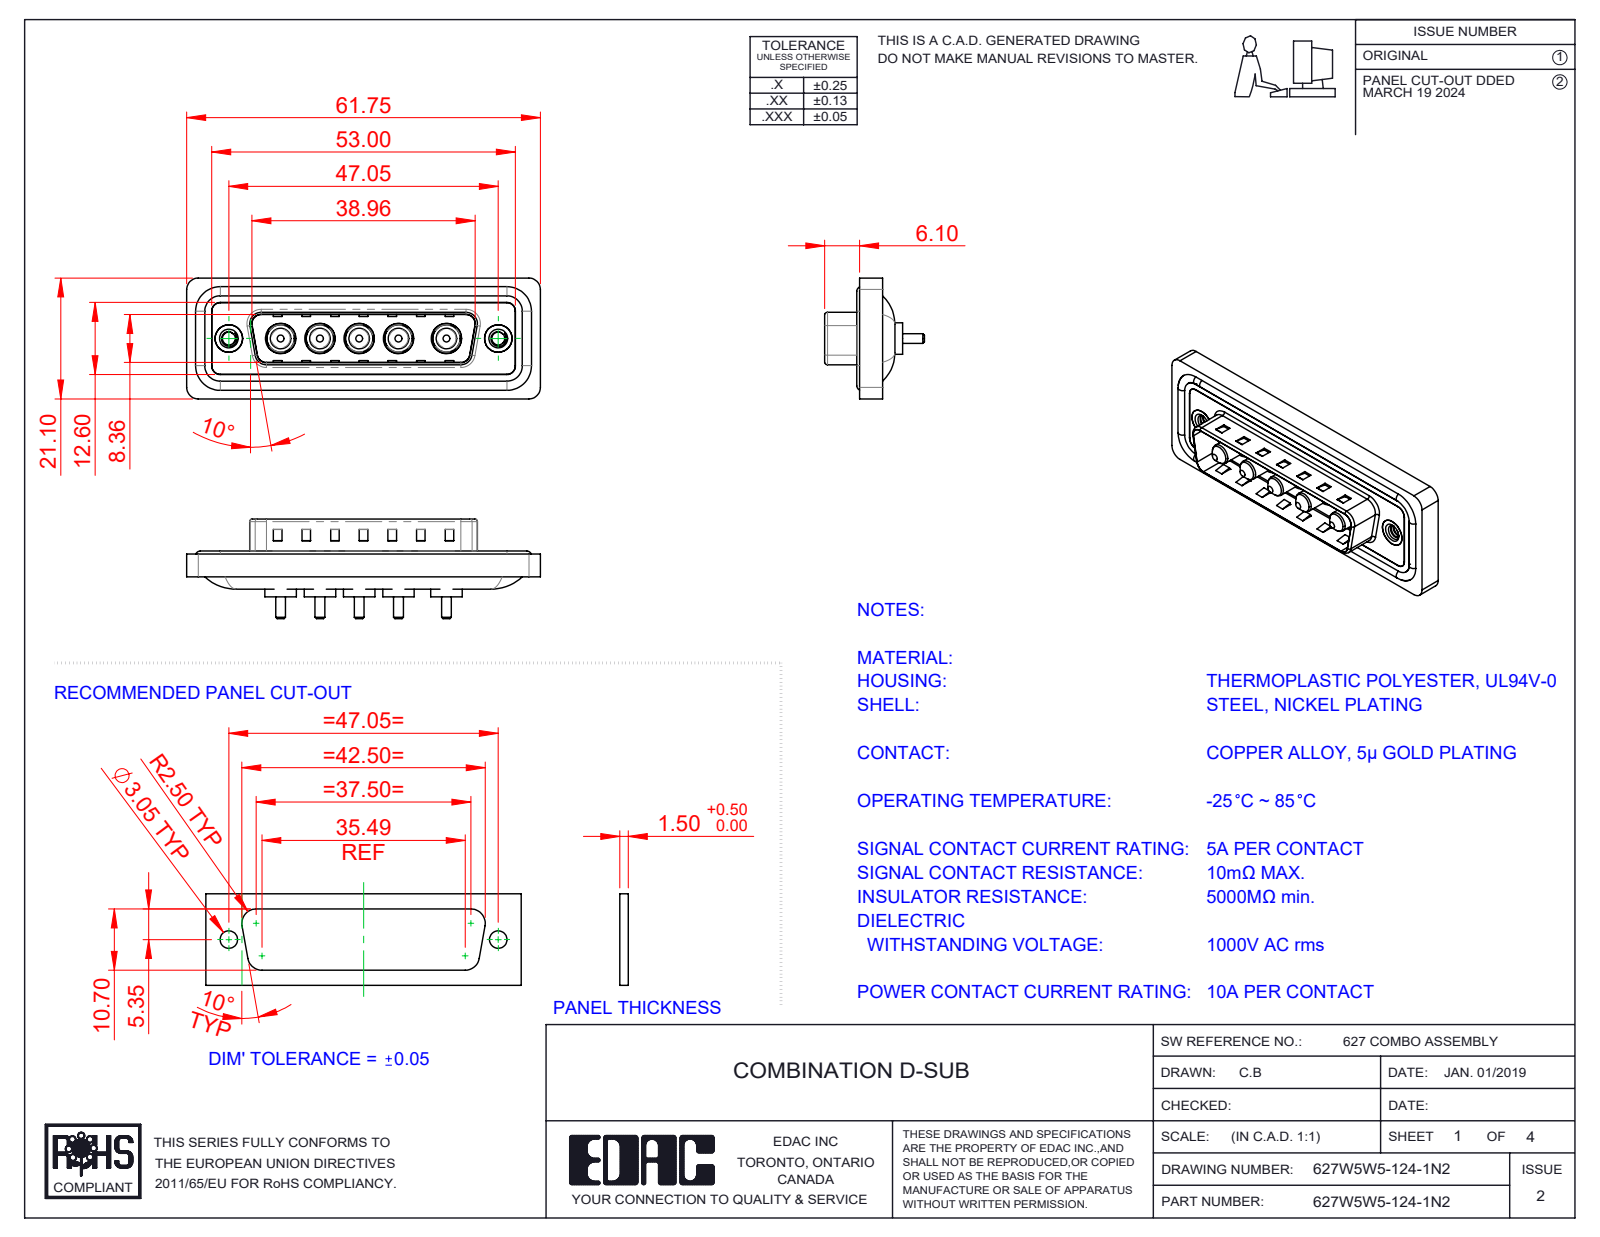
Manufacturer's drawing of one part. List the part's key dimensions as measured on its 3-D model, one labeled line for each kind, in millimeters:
Part name (STEP PRODUCT): 627W5W5-124-1N2; 627Combo Shell Rear_25 Contacts; 627Combo Threaded Rivet_2; 627Combo Waterproof Housing_25 Contacts (+3 more)
STEP written by: SolidWorks 2023 (CONFIG_CONTROL_DESIGN)
Units: millimetres
Bodies: 17 solids, 678 faces (259 planar, 283 cylindrical, 136 other)
Overall size (bounding box): 61.75 × 21.1 × 17.4
Volume: 7 399 mm³ · Surface area: 11 733 mm²
Round holes (diameter × count): ⌀4.85 ×5, ⌀5.3 ×5, ⌀2.26 ×2, ⌀4 ×2, ⌀4.8 ×2, ⌀5 ×2
Round bosses / shafts (diameter × count): ⌀5.5 ×5, ⌀5.2 ×5, ⌀4.75 ×5, ⌀3.75 ×5, ⌀3.6 ×5, ⌀1.7 ×5, ⌀1.6 ×4, ⌀4.9 ×2
Partial cylindrical surfaces — rounded edges, fillets, slot ends (radius × count): R1.5 ×22, R2 ×18, R0.5 ×8, R1.6 ×8, R2.1 ×5, R0.25 ×4, R0.6 ×4, R0.65 ×4
Main face-to-face distances: 0.4, 1.5, 0.5, 1.1, 3.1, 1.6, 2.9, 0.82, 9.58, 5.65
Hole centre spacings: 6.86, 9.04, 13.73, 38.01, 6.87, 8.37, 8.38, 9.05
